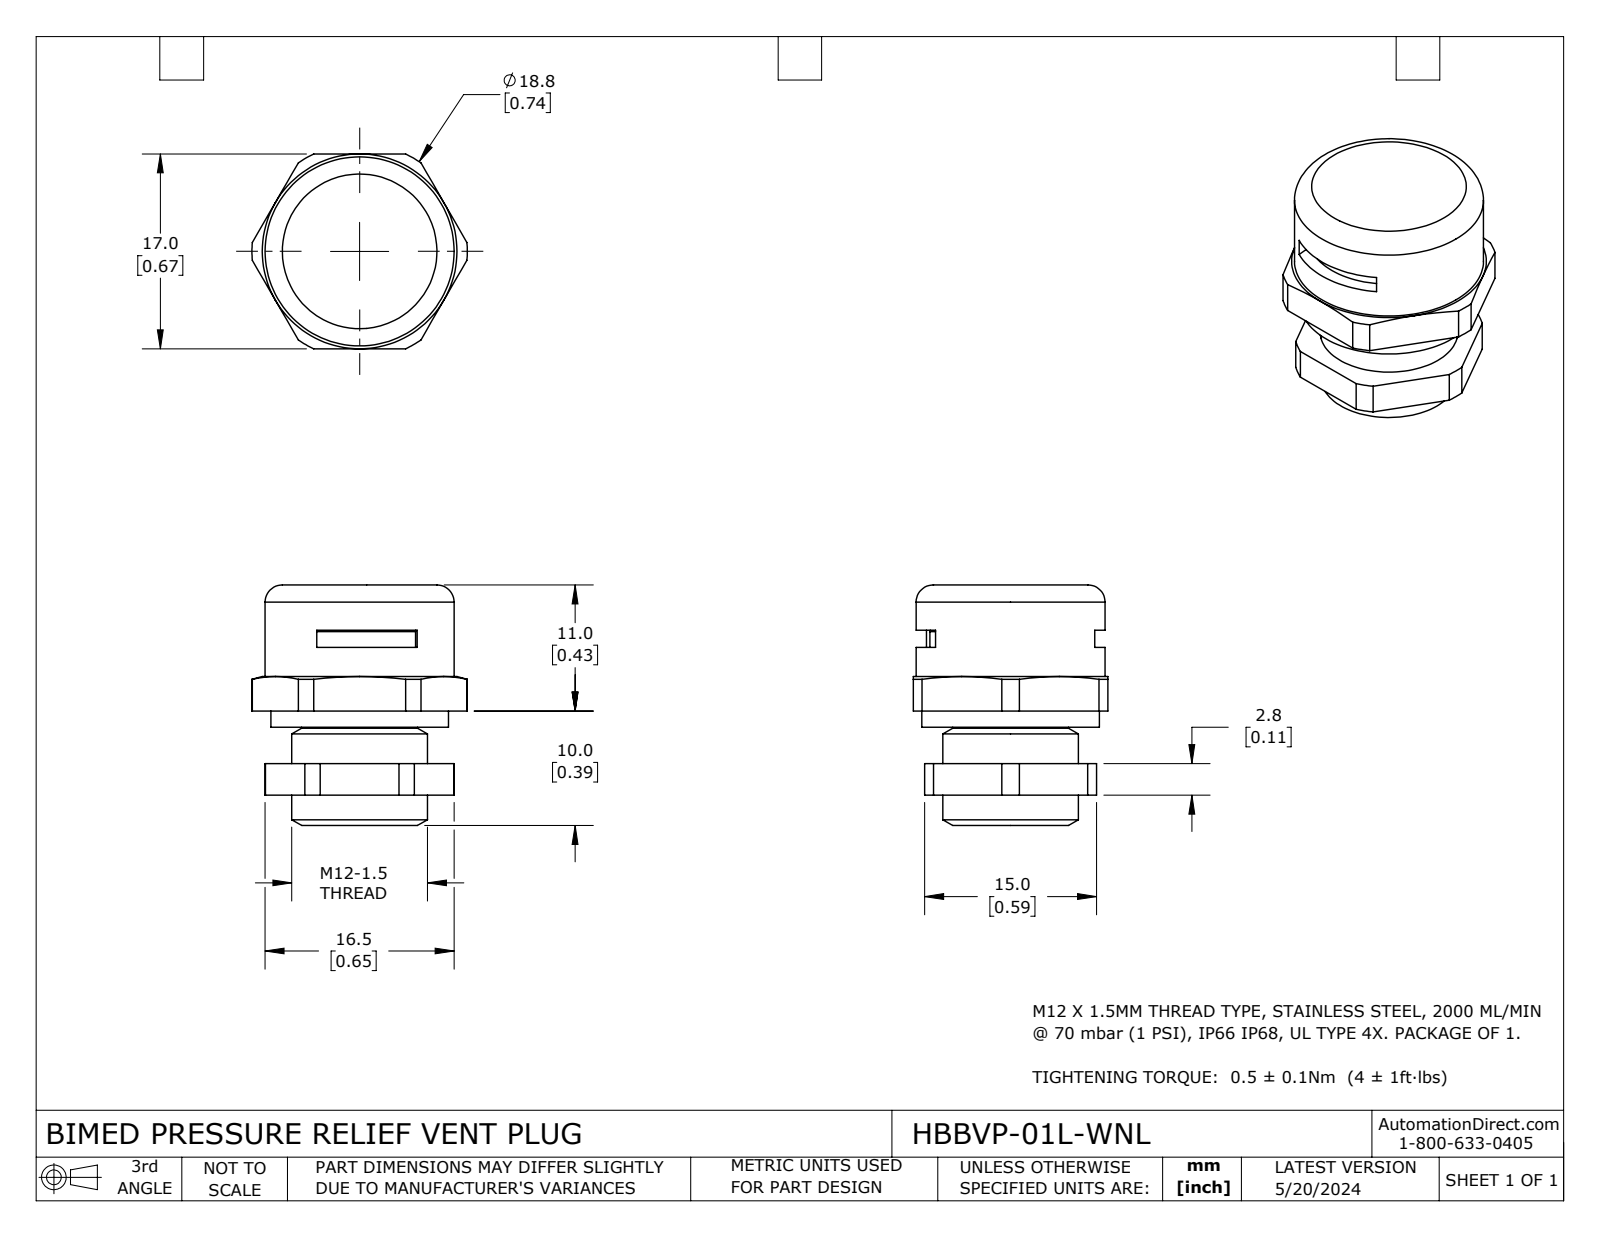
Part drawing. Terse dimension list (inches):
name: HBBVP-01L-WNL
written by: SolidWorks 2023 (CONFIG_CONTROL_DESIGN)
unit: in
bodies: 3 solids, 82 faces (29 planar, 30 cylindrical, 23 other)
size: 0.827 × 0.74 × 0.669
volume: 0.237 in³; area: 3.534 in²
holes: 1× ⌀0.394, 1× ⌀0.472
bosses: 1× ⌀0.65, 1× ⌀0.61, 1× ⌀0.467, 1× ⌀0.398
rounds: 1× R0.278, 1× R0.37
face distances: 0.433, 0.039, 0.63, 0.056, 0.489, 0.338, 0.394, 0.827, 0.105, 0.233
